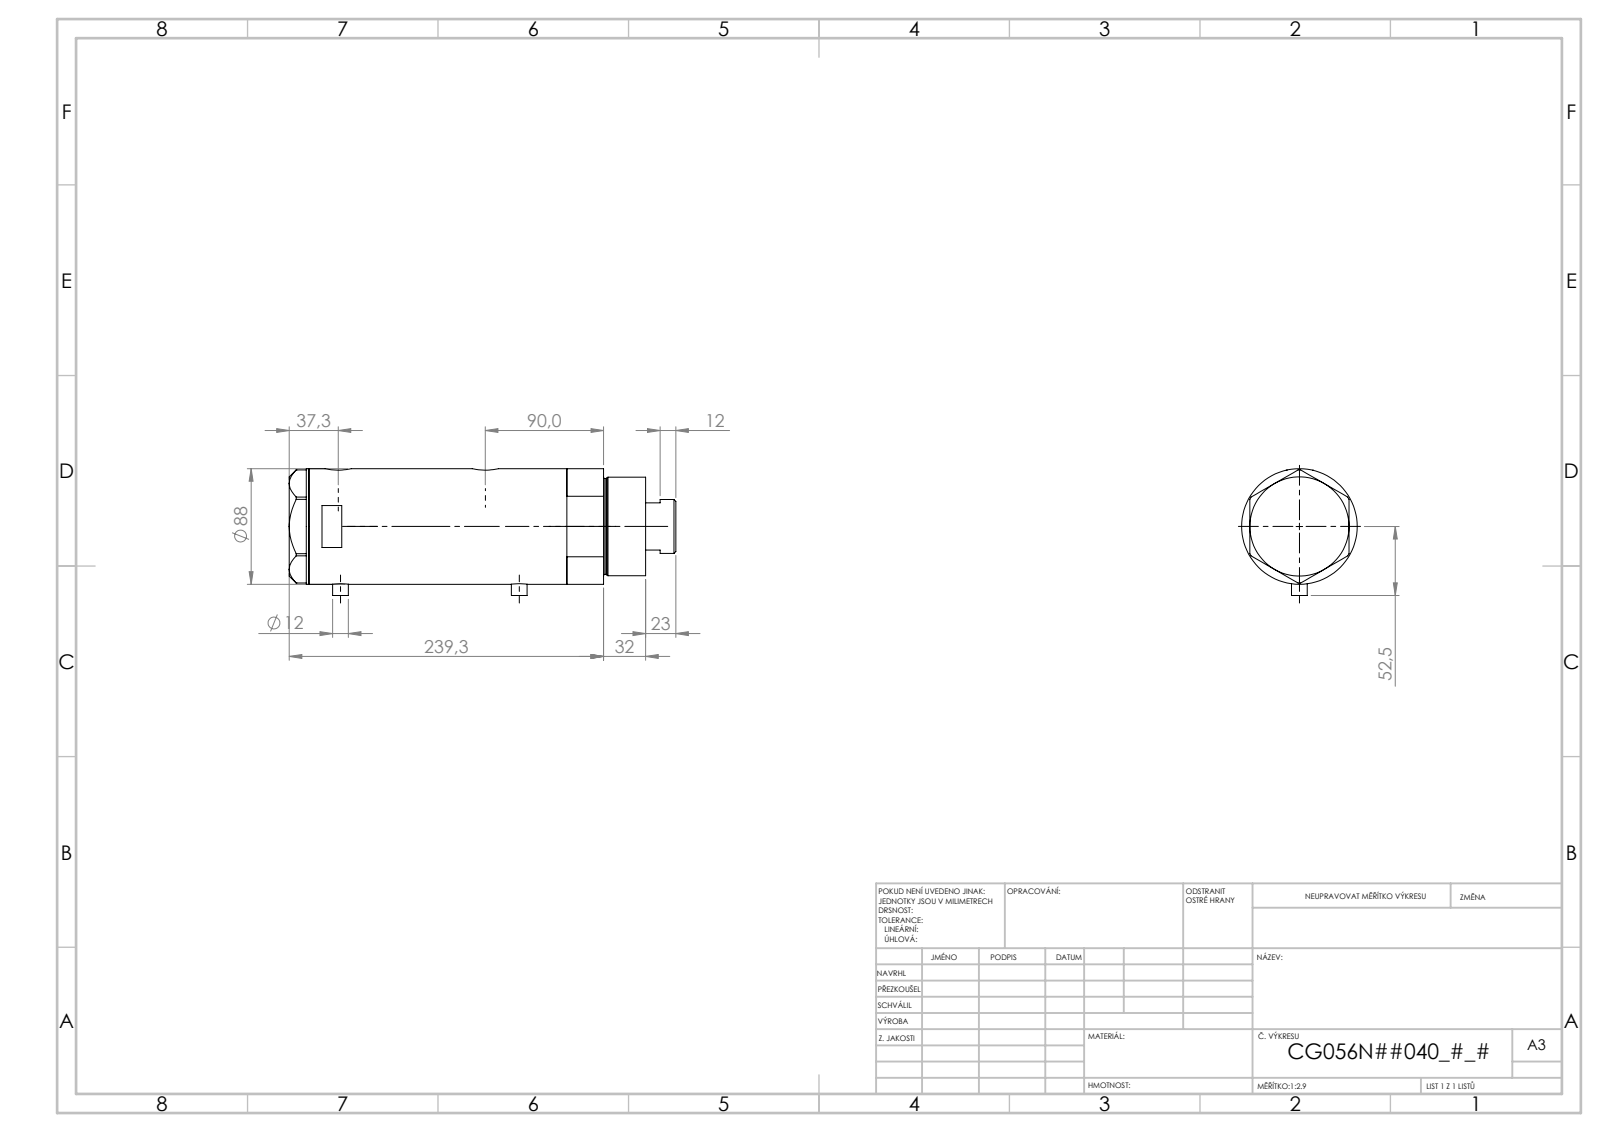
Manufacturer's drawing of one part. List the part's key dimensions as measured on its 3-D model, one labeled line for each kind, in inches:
Part name (STEP PRODUCT): V270CG_FRONT; V270CG_MIDDLE; V270CG_BACK; V270CG_VC
STEP written by: SolidWorks 2019 (CONFIG_CONTROL_DESIGN)
Units: inches
Bodies: 4 solids, 121 faces (52 planar, 49 cylindrical, 20 other)
Overall size (bounding box): 11.587 × 3.799 × 3.465
Volume: 94.28 in³ · Surface area: 343.9 in²
Round holes (diameter × count): ⌀0.492 ×2, ⌀0.518 ×2, ⌀0.787 ×2, ⌀0.571 ×1, ⌀1.654 ×1, ⌀1.713 ×1, ⌀2.205 ×1, ⌀2.362 ×1, ⌀3.15 ×1
Round bosses / shafts (diameter × count): ⌀0.472 ×2, ⌀3.465 ×1, ⌀2.953 ×1, ⌀2.874 ×1, ⌀1.614 ×1
Main face-to-face distances: 5.291, 1.024, 4.268, 0.591, 1.614, 5.882, 10.091, 10.681, 9.067, 4.799
Hole centre spacings: 0.067, 1.016, 4.343, 4.409, 5.358, 5.425
